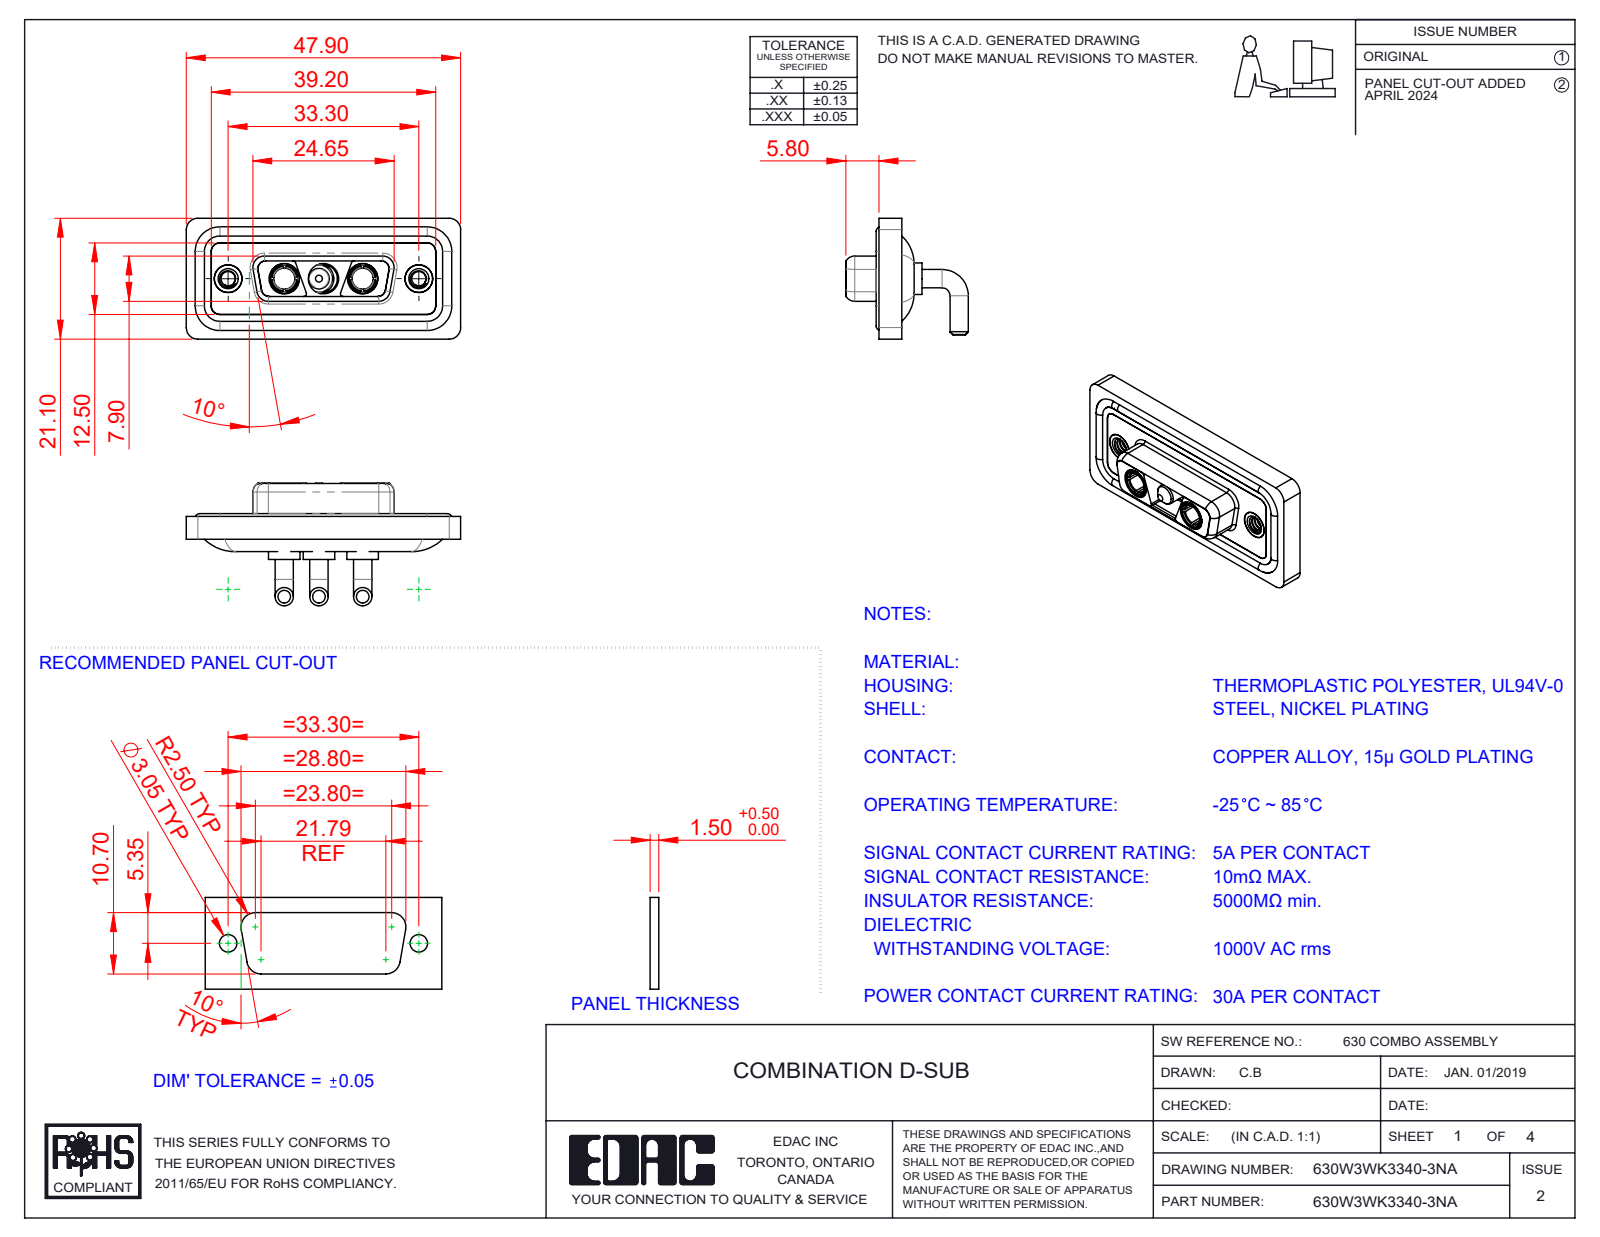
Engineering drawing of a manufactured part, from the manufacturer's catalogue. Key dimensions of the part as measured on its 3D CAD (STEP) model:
Part name (STEP PRODUCT): Power Socket_30A RA; 630Combo Housing_3WK3; 630Combo Shell Front_15 Contacts; 630Combo Waterproof Housing_15 Contacts (+4 more)
STEP written by: SolidWorks 2023 (CONFIG_CONTROL_DESIGN)
Units: millimetres
Bodies: 13 solids, 589 faces (178 planar, 262 cylindrical, 149 other)
Overall size (bounding box): 47.9 × 21.4 × 21.1
Volume: 6 109 mm³ · Surface area: 9 797 mm²
Round holes (diameter × count): ⌀4.85 ×5, ⌀5.3 ×3, ⌀2.5 ×2, ⌀3.7 ×2, ⌀4 ×2, ⌀4.05 ×2, ⌀5 ×2
Round bosses / shafts (diameter × count): ⌀3.2 ×6, ⌀1.6 ×4, ⌀5.5 ×3, ⌀5.2 ×3, ⌀4.75 ×3, ⌀3.75 ×3, ⌀4.96 ×2, ⌀4.95 ×2
Partial cylindrical surfaces — rounded edges, fillets, slot ends (radius × count): R2 ×20, R1.5 ×18, R1.35 ×12, R0.5 ×8, R1.6 ×8, R0.25 ×4, R0.6 ×4, R0.65 ×4
Main face-to-face distances: 0.4, 1.8, 1.1, 1.6, 2.9, 2.5, 3.1, 3.7, 4.1, 1.5
Hole centre spacings: 6.85, 9.8, 16.65, 23.5, 13.7, 33.3
